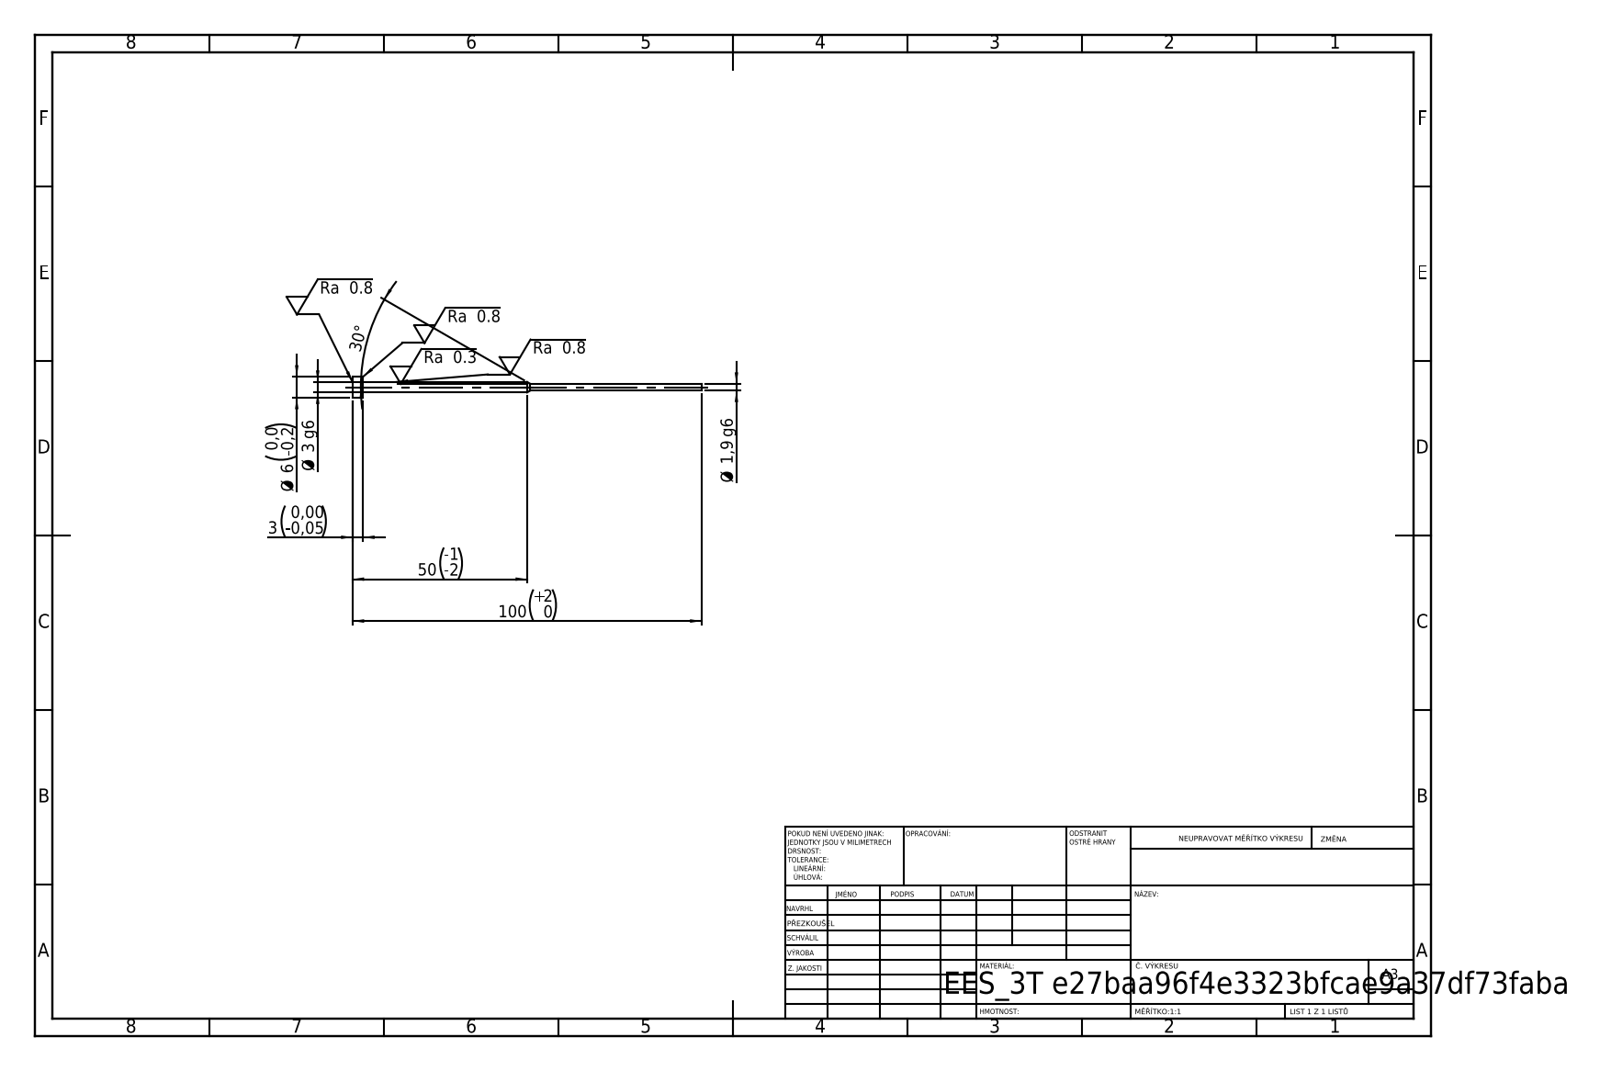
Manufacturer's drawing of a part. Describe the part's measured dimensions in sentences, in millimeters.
Its 3-D file was written by "SolidWorks 2019 (CONFIG_CONTROL_DESIGN)". It is 1 solid with 11 faces: 3 planar, 6 cylindrical and 2 other. Overall it measures 100 by 6 by 6 millimeters. Its volume is 561 cubic millimeters and its surface area 853 square millimeters. Round bosses or shafts: 1 of diameter 6, 1 of diameter 3, 1 of diameter 1.9. The main face-to-face distances are 3, 97, 100.
